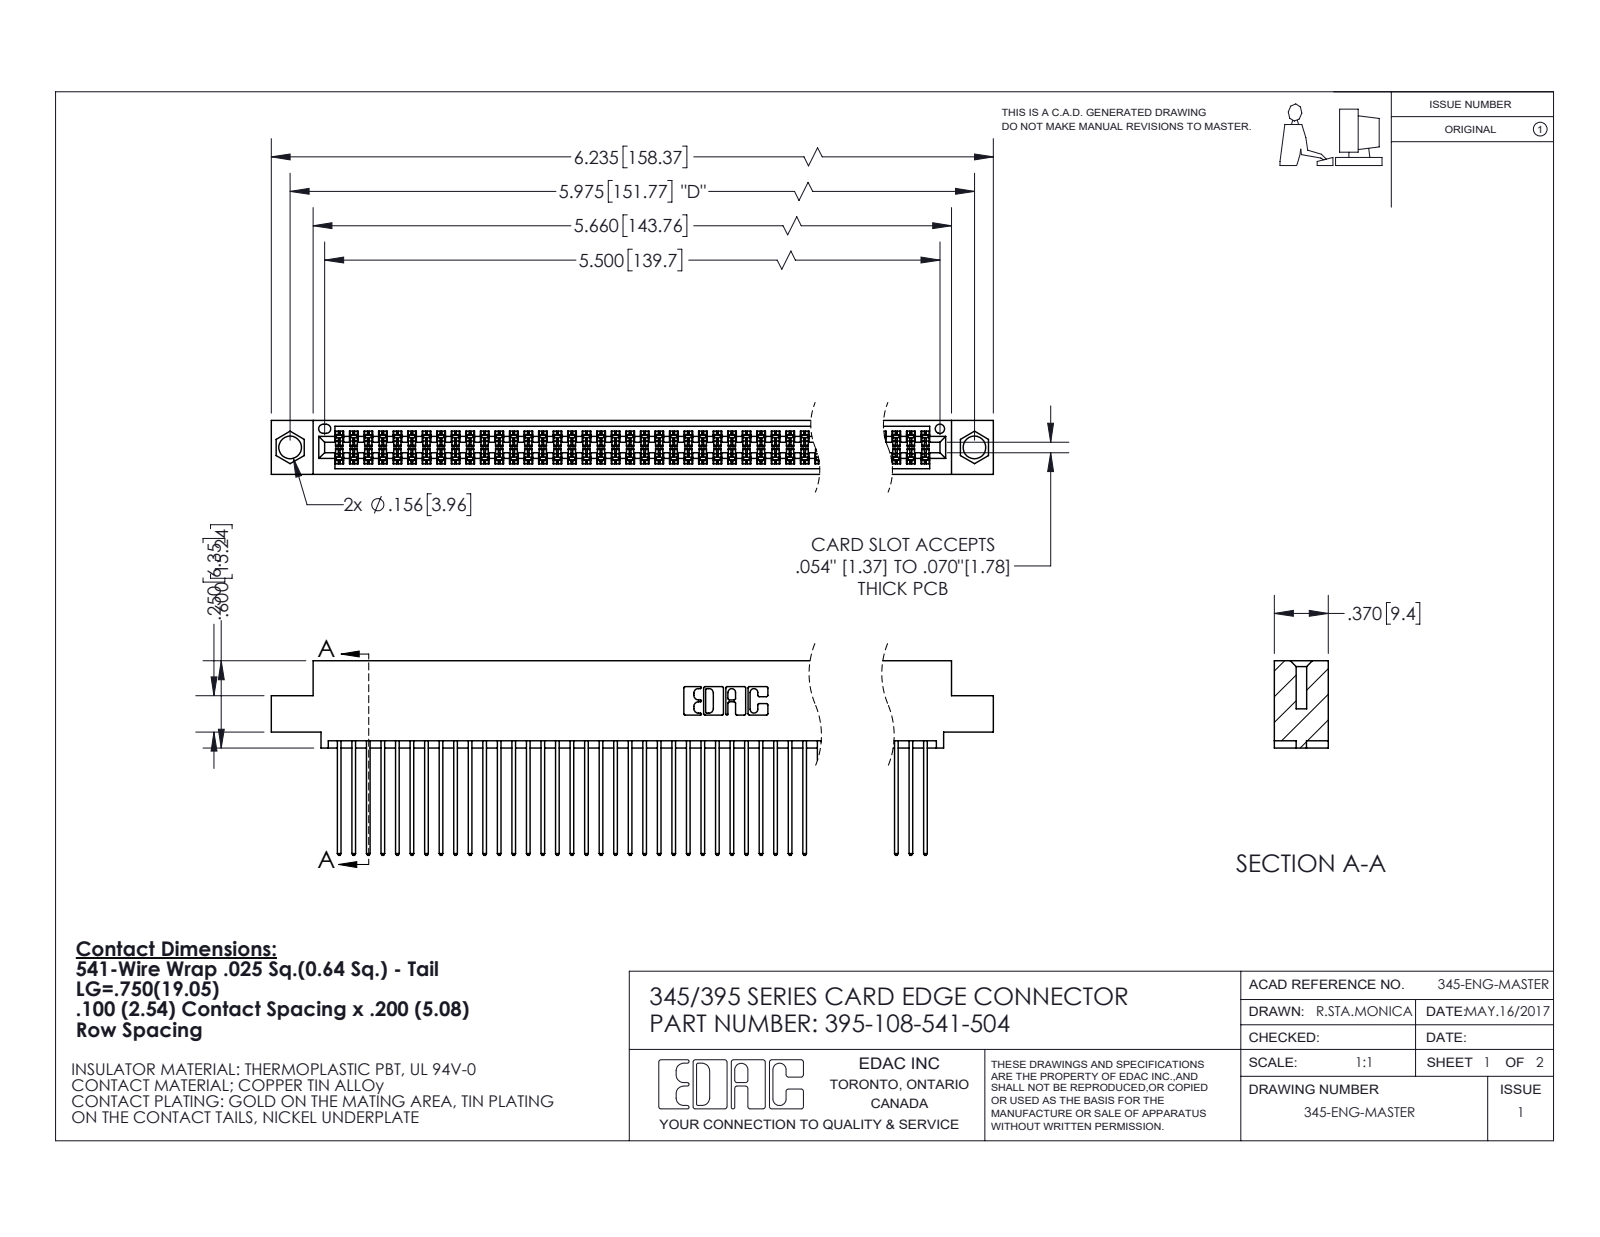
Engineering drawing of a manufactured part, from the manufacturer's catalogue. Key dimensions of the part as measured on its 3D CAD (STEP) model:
Part name (STEP PRODUCT): 395-108-541-504; 345-292-001_345-293-141; 345 Part_0.110 Offset - 0.156 Dia-TI
STEP written by: SolidWorks 2020 (CONFIG_CONTROL_DESIGN)
Units: inches
Bodies: 109 solids, 5544 faces (3662 planar, 1882 cylindrical, 0 other)
Overall size (bounding box): 6.235 × 1.337 × 0.37
Volume: 0.972 in³ · Surface area: 41.3 in²
Round holes (diameter × count): ⌀0.156 ×2, ⌀0.064 ×1
Partial cylindrical surfaces — rounded edges, fillets, slot ends (radius × count): R0.006 ×162, R0.01 ×108, R0.01 ×22, R0.007 ×6, R0.031 ×6, R0.026 ×3, R0.014 ×2, R0.019 ×2
Main face-to-face distances: 0.298, 0.072, 0.2, 0.098, 0.272, 0.025, 0.225, 0.37, 0.175, 0.149
Hole centre spacings: 0.27, 5.739, 5.975
